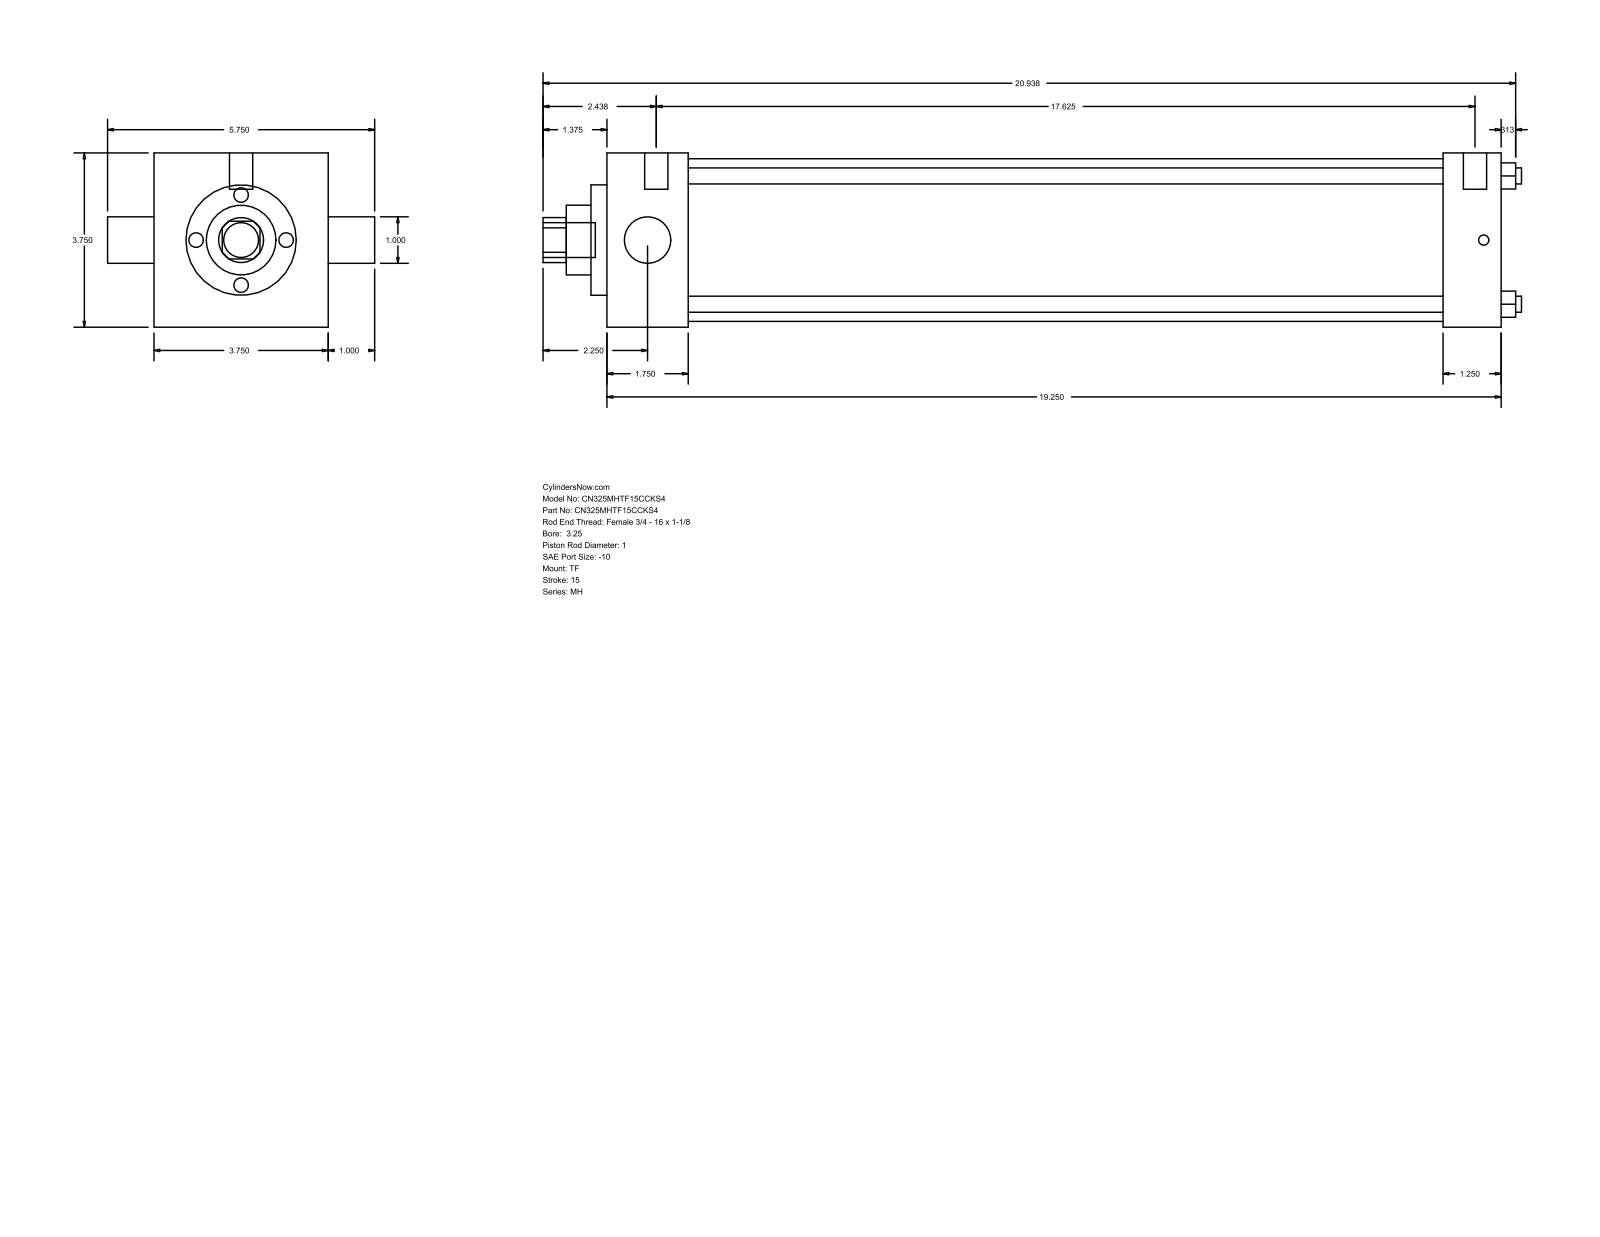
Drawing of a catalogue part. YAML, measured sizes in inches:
part_name: "MH_TF__0325_1"
step_written_by: "GSSL Pune (CONFIG_CONTROL_DESIGN)"
units: inches
bodies: {solids: 0, faces: 86, planar: 61, cylindrical: 25, other: 0}
overall_size: [21.063, 5.75, 3.75]
round_holes:
  - {diameter: 0.345, count: 4}
  - {diameter: 1, count: 2}
  - {diameter: 1.5, count: 1}
  - {diameter: 2.375, count: 1}
  - {diameter: 3.5, count: 1}
round_bosses_or_shafts:
  - {diameter: 0.219, count: 3}
  - {diameter: 0.5, count: 2}
  - {diameter: 0.75, count: 1}
partial_cylinders:
  - {radius: 0.484, count: 1}
face_to_face_distances: [3.75, 19.25, 1.75, 18, 16.25, 17.5, 1.25, 0.344, 2.094, 18.344]
hole_center_spacings: [1.952, 2.76, 3.903]
